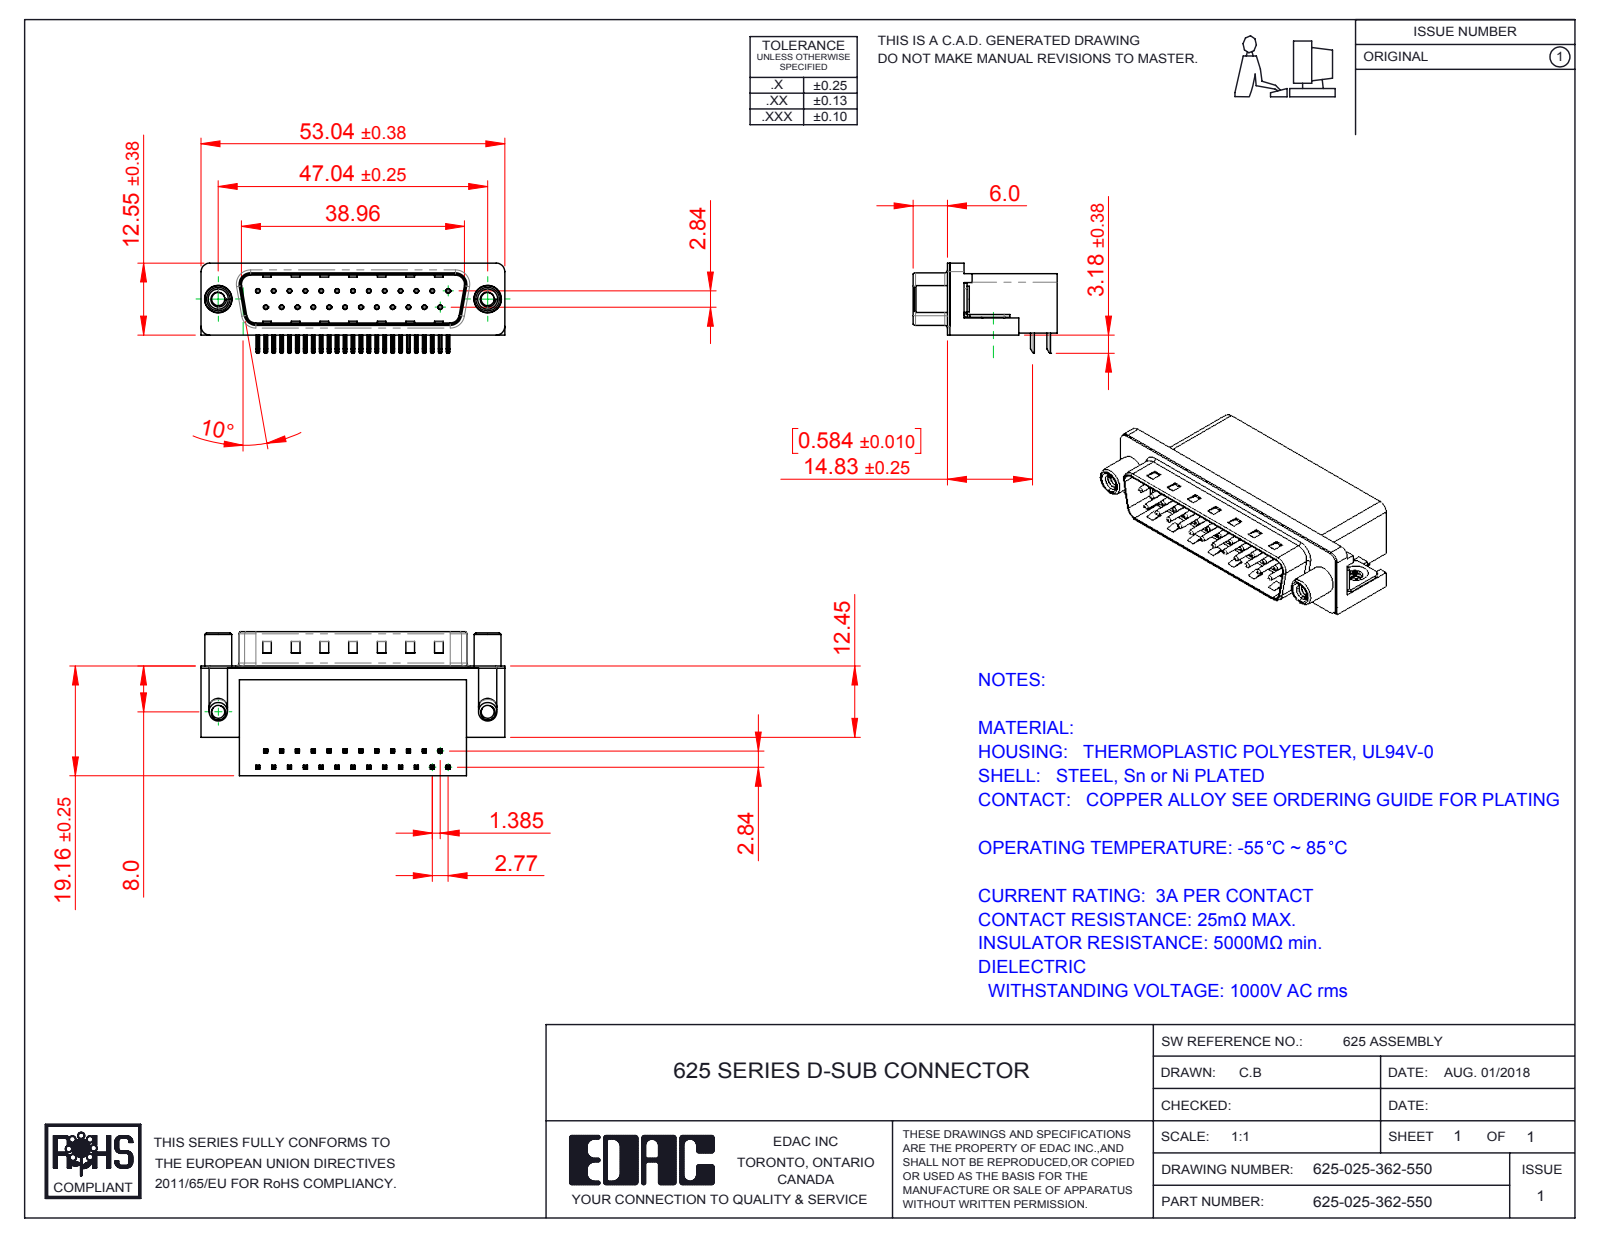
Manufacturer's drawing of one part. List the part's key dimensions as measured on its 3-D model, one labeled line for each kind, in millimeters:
Part name (STEP PRODUCT): 625 Shell_25 Socket; 625 Contact Bottom; 625 Round Threaded Standoff; 625 Housing_25 Socket (+3 more)
STEP written by: SolidWorks 2016 (CONFIG_CONTROL_DESIGN)
Units: millimetres
Bodies: 31 solids, 2291 faces (1399 planar, 681 cylindrical, 211 other)
Overall size (bounding box): 53.04 × 25.16 × 15.73
Volume: 9 266 mm³ · Surface area: 9 140 mm²
Round holes (diameter × count): ⌀0.35 ×25, ⌀0.8 ×25, ⌀2.26 ×2, ⌀2.3 ×2, ⌀3.1 ×2, ⌀4 ×2, ⌀4.8 ×2, ⌀5 ×2
Round bosses / shafts (diameter × count): ⌀0.75 ×25, ⌀4.9 ×2, ⌀4.7 ×2, ⌀4.5 ×2, ⌀3.85 ×2, ⌀3.26 ×2
Partial cylindrical surfaces — rounded edges, fillets, slot ends (radius × count): R0.25 ×100, R0.12 ×50, R1 ×16, R0.5 ×9, R1.6 ×8, R1.5 ×7, R0.9 ×4, R2 ×4
Main face-to-face distances: 0.4, 10.35, 18.76, 2.1, 8.76, 10.46, 10.86, 1.7, 19.16, 2.9
Hole centre spacings: 3.16, 2.77, 11.08, 5.54, 8.31, 5.03, 13.85, 7.48
